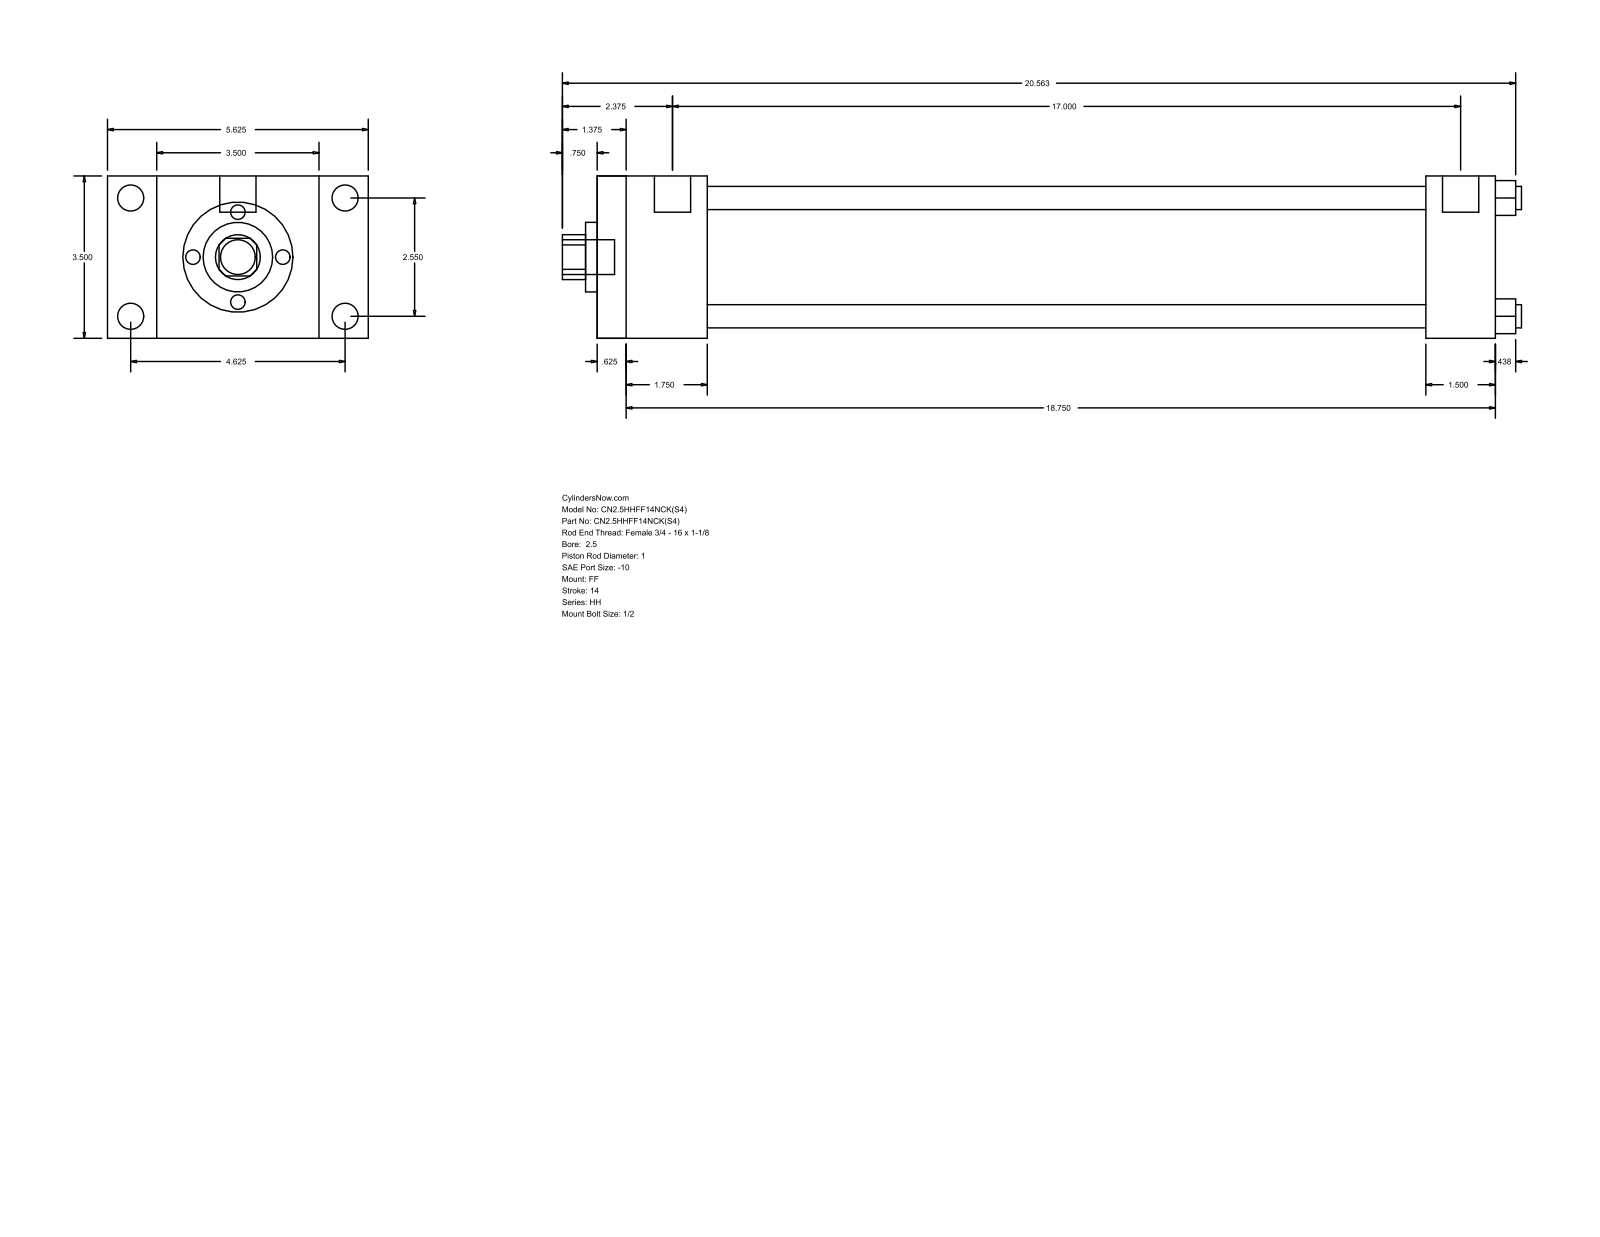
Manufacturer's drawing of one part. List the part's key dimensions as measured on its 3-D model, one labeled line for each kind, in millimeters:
Part name (STEP PRODUCT): HH_FF__0250_1
STEP written by: GSSL Pune (CONFIG_CONTROL_DESIGN)
Units: millimetres
Bodies: 0 solids, 92 faces (64 planar, 28 cylindrical, 0 other)
Overall size (bounding box): 525.46 × 142.88 × 88.9
Round holes (diameter × count): ⌀12.7 ×4, ⌀25.4 ×1, ⌀38.1 ×1, ⌀73.03 ×1
Round bosses / shafts (diameter × count): ⌀14.3 ×4, ⌀5.56 ×4, ⌀19.84 ×2, ⌀19.05 ×1
Partial cylindrical surfaces — rounded edges, fillets, slot ends (radius × count): R12.29 ×1
Main face-to-face distances: 88.9, 492.13, 15.87, 476.26, 60.33, 44.46, 431.8, 454.02, 438.15, 393.69
Hole centre spacings: 45.79, 64.76, 91.58
